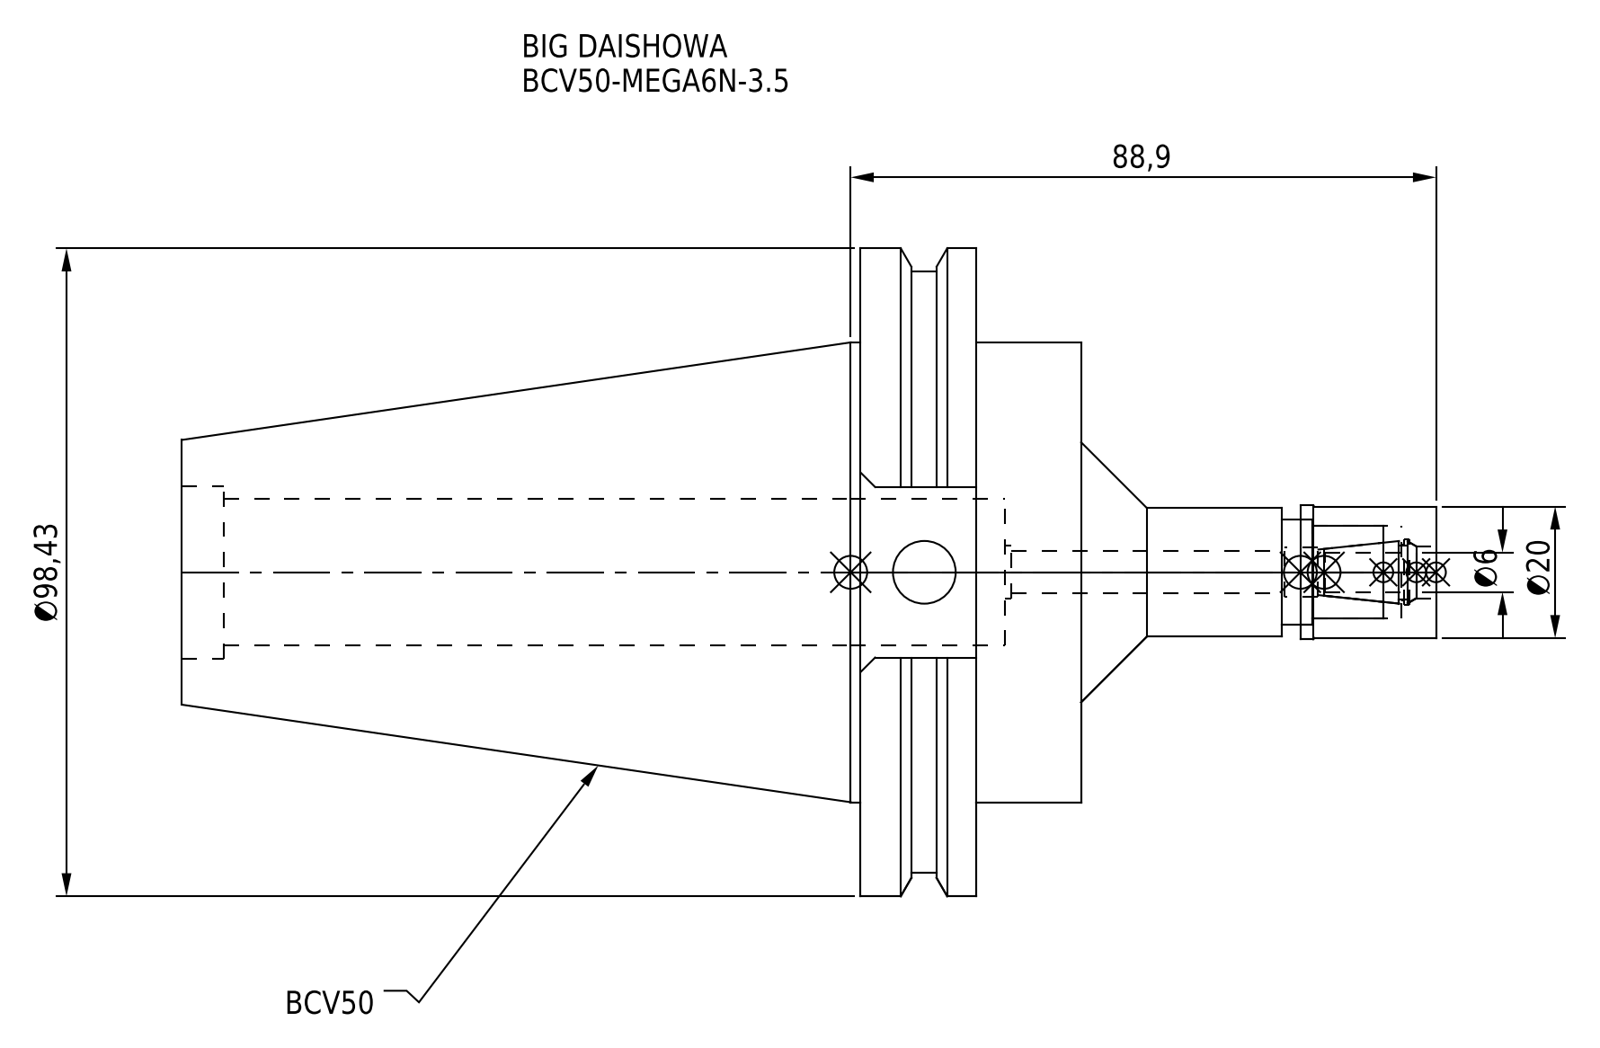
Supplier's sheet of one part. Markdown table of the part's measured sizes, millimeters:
| quantity | value |
| --- | --- |
| part name | DXF_TEMP_ASSY_ASM_4_ASM.stp; BCV50-MEGA6N-3_5-060.stp; BCV50MN06035-060_ASM.stp; BCV50-MEGA6N-3_5 (+3 more) |
| STEP written by | SolidWorks 2019 (CONFIG_CONTROL_DESIGN) |
| units | millimeters |
| bodies | 2 solids, 91 faces (33 planar, 44 cylindrical, 14 other) |
| overall size | 190.5 × 98.42 × 94.95 |
| volume | 399 921 mm³ |
| surface area | 55 124 mm² |
| round holes (diameter × count) | 6.4 × 1, 7.5 × 1, 7.9 × 1, 8 × 1, 8.5 × 1, 9.53 × 1, 10 × 1, 14 × 1, 16 × 1, 22.3 × 1, 26.23 × 1 |
| round bosses / shafts (diameter × count) | 98.42 × 1, 91.29 × 1, 69.85 × 1, 20.3 × 1, 20 × 1, 19.5 × 1 |
| main face-to-face distances | 17.55, 15.95, 33.5, 136.6, 120.65, 103.1, 72.95, 11.6, 4.35, 21.9 |
